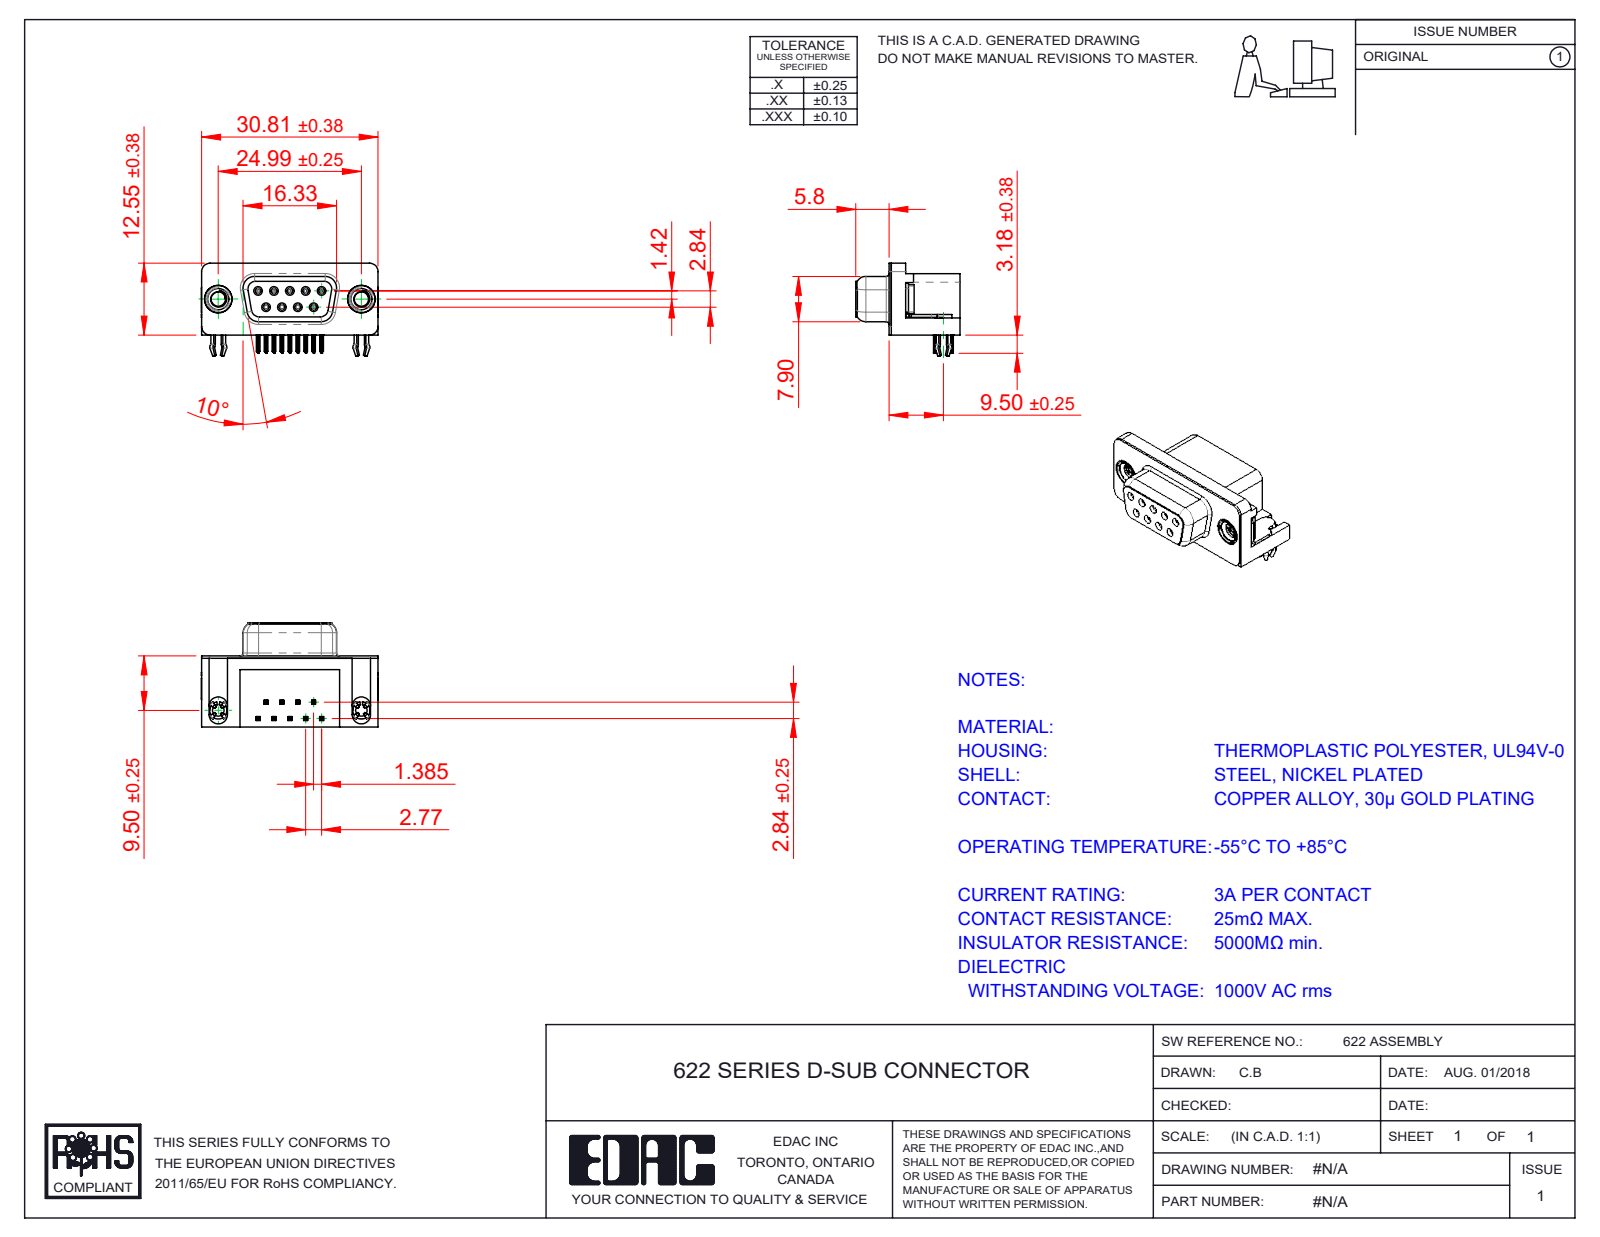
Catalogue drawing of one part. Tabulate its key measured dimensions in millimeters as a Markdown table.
| quantity | value |
| --- | --- |
| part name | 622 M3 Threaded Rivet; 622 Socket Bottom; 622 Housing_9 Socket; 622 Shell_9 Socket (+3 more) |
| STEP written by | SolidWorks 2016 (CONFIG_CONTROL_DESIGN) |
| units | millimeters |
| bodies | 15 solids, 1602 faces (684 planar, 432 cylindrical, 486 other) |
| overall size | 30.89 × 18.2 × 15.73 |
| volume | 3 732 mm³ |
| surface area | 5 156 mm² |
| round holes (diameter × count) | 0.8 × 9, 0.9 × 9, 2.26 × 2, 2.5 × 2, 4 × 2, 4.8 × 2, 5 × 2 |
| round bosses / shafts (diameter × count) | 1.2 × 9, 4.9 × 2, 4.75 × 2, 3.9 × 2, 3.26 × 2 |
| partial cylindrical surfaces (radius × count) | 0.1 × 72, 0.15 × 36, 0.35 × 18, 1 × 18, 0.34 × 9, 0.25 × 8, 1.35 × 8, 1.6 × 8 |
| main face-to-face distances | 0.4, 12, 12.4, 0.35, 2.9, 2.5, 6.2, 10.34, 9.5, 5.8 |
| hole center spacings | 3.16, 2.77, 5.54, 5.03, 5.04, 8.31, 7.48, 7.49 |
